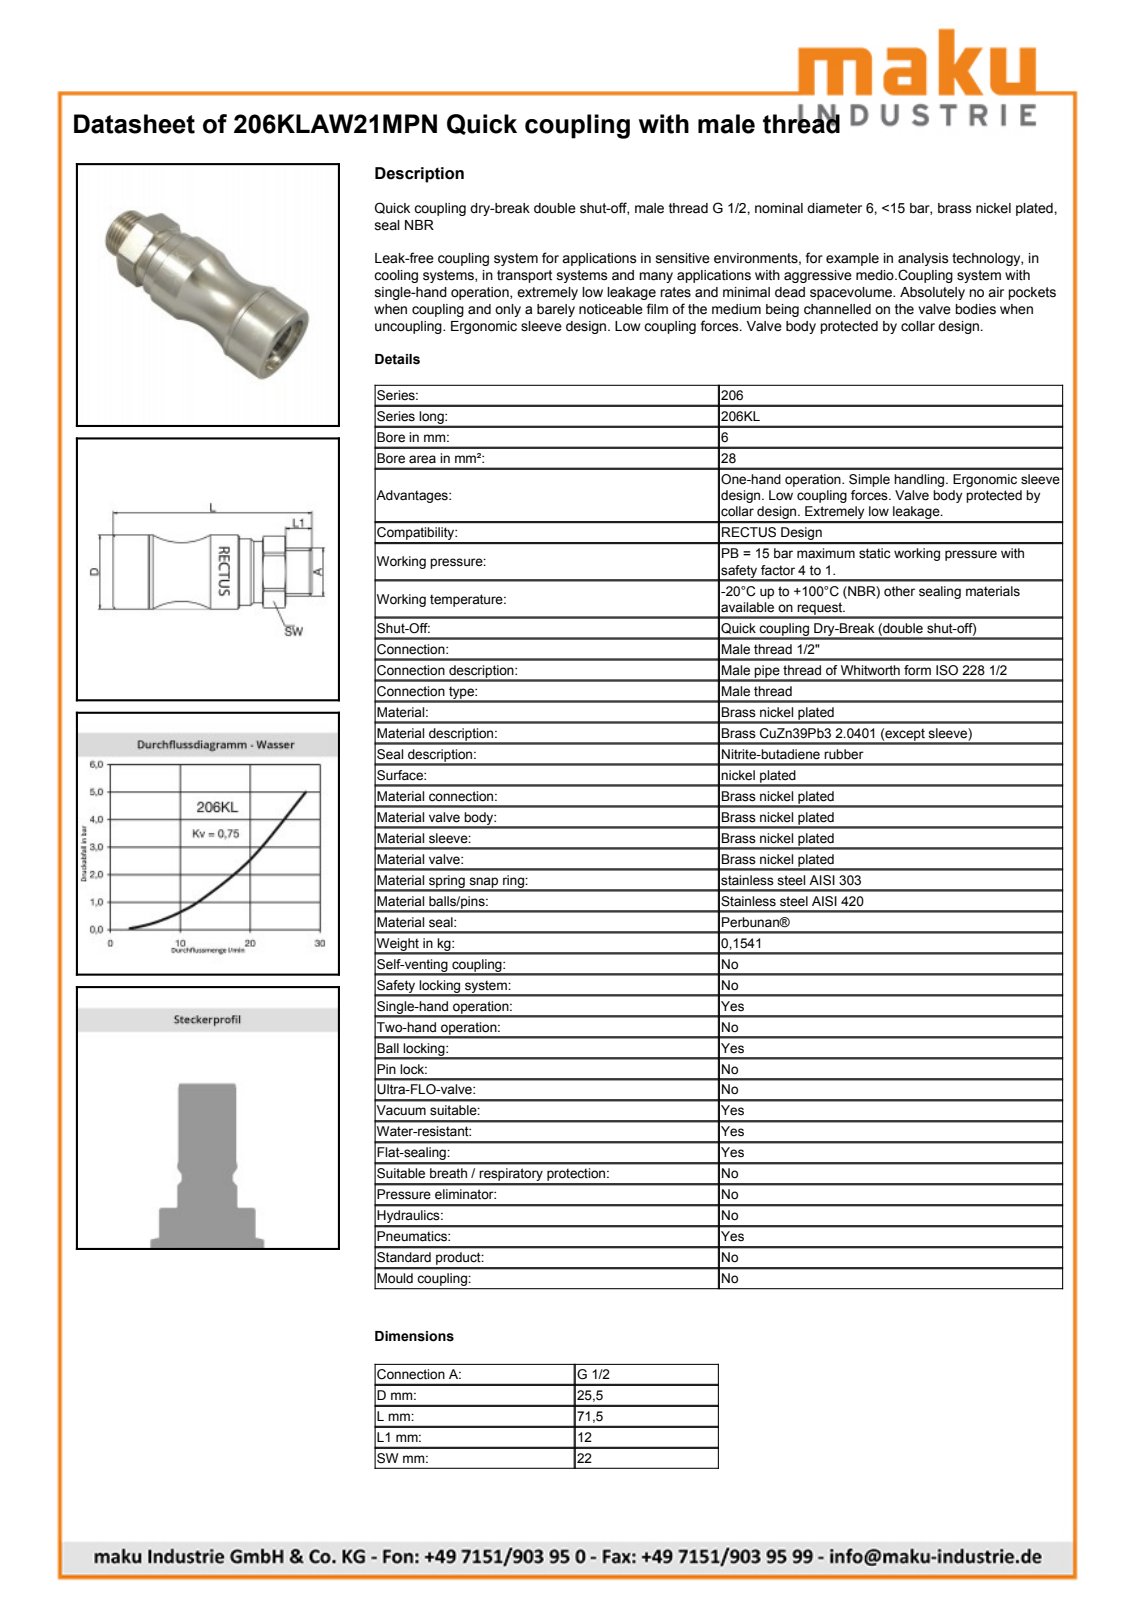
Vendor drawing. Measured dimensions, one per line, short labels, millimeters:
name: D108390
written by: Autodesk Inventor 2013 (AUTOMOTIVE_DESIGN)
unit: mm
bodies: 2 solids, 1173 faces (417 planar, 145 cylindrical, 611 other)
size: 71.5 × 26.94 × 25.5
volume: 26 196 mm³; area: 14 172 mm²
holes: 1× ⌀18.1, 1× ⌀18.15, 1× ⌀18.25, 1× ⌀19.7, 1× ⌀20.05, 1× ⌀20.9, 1× ⌀21.3, 1× ⌀23.1, 1× ⌀23.55, 1× ⌀24.1
bosses: 1× ⌀25.5, 1× ⌀25.3, 1× ⌀23.4, 1× ⌀23, 1× ⌀21, 1× ⌀20.95, 1× ⌀20, 1× ⌀18
rounds: 1× R13.53
face distances: 71.5, 24, 8, 4.1, 51.5, 20, 59.5, 12, 4.65, 1.3
